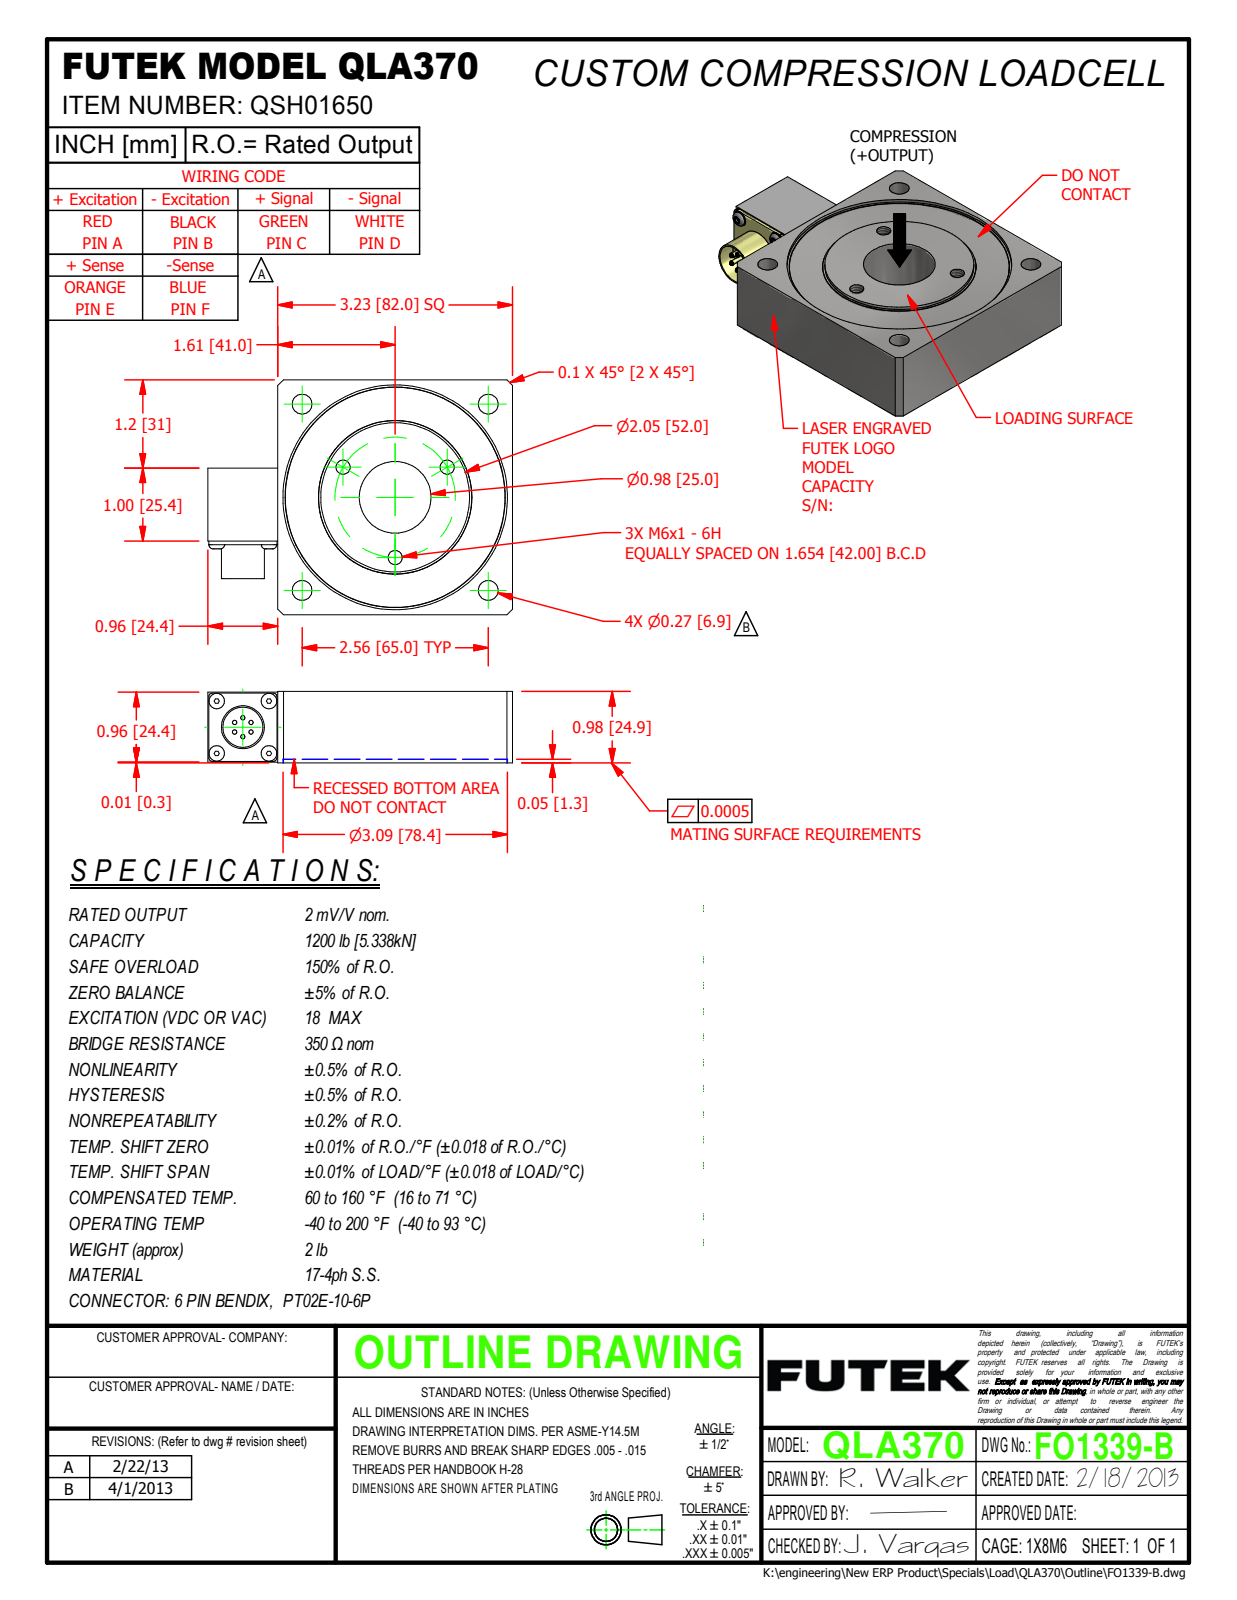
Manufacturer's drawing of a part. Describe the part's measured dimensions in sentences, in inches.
The part is named "FO1339-A". Its 3-D file was written by "Autodesk Inventor 2015 (AUTOMOTIVE_DESIGN)". It is 1 solid with 118 faces: 68 planar, 36 cylindrical and 14 other. Overall it measures 4.188 by 3.228 by 0.98 inches. Its volume is 9.483 cubic inches and its surface area 47.76 square inches. Round holes: 4 of diameter 0.272, 3 of diameter 0.194, 1 of diameter 0.55, 1 of diameter 0.984, 1 of diameter 2.11, 1 of diameter 3.027, 1 of diameter 3.087. Round bosses or shafts: 6 of diameter 0.06, 4 of diameter 0.213, 1 of diameter 3.022, 1 of diameter 2.107, 1 of diameter 2.047, 1 of diameter 0.59. Partial cylindrical surfaces (rounded edges, fillets, slot ends): 4 of radius 0.05. The main face-to-face distances are 0.045, 0.885, 3.228, 0.841, 0.095, 0.935, 0.98, 0.05, 0.93, 0.96. The hole center spacings are 1.809, 2.559, 0.827, 1.033, 1.357, 1.432, 1.784, 2.176.
